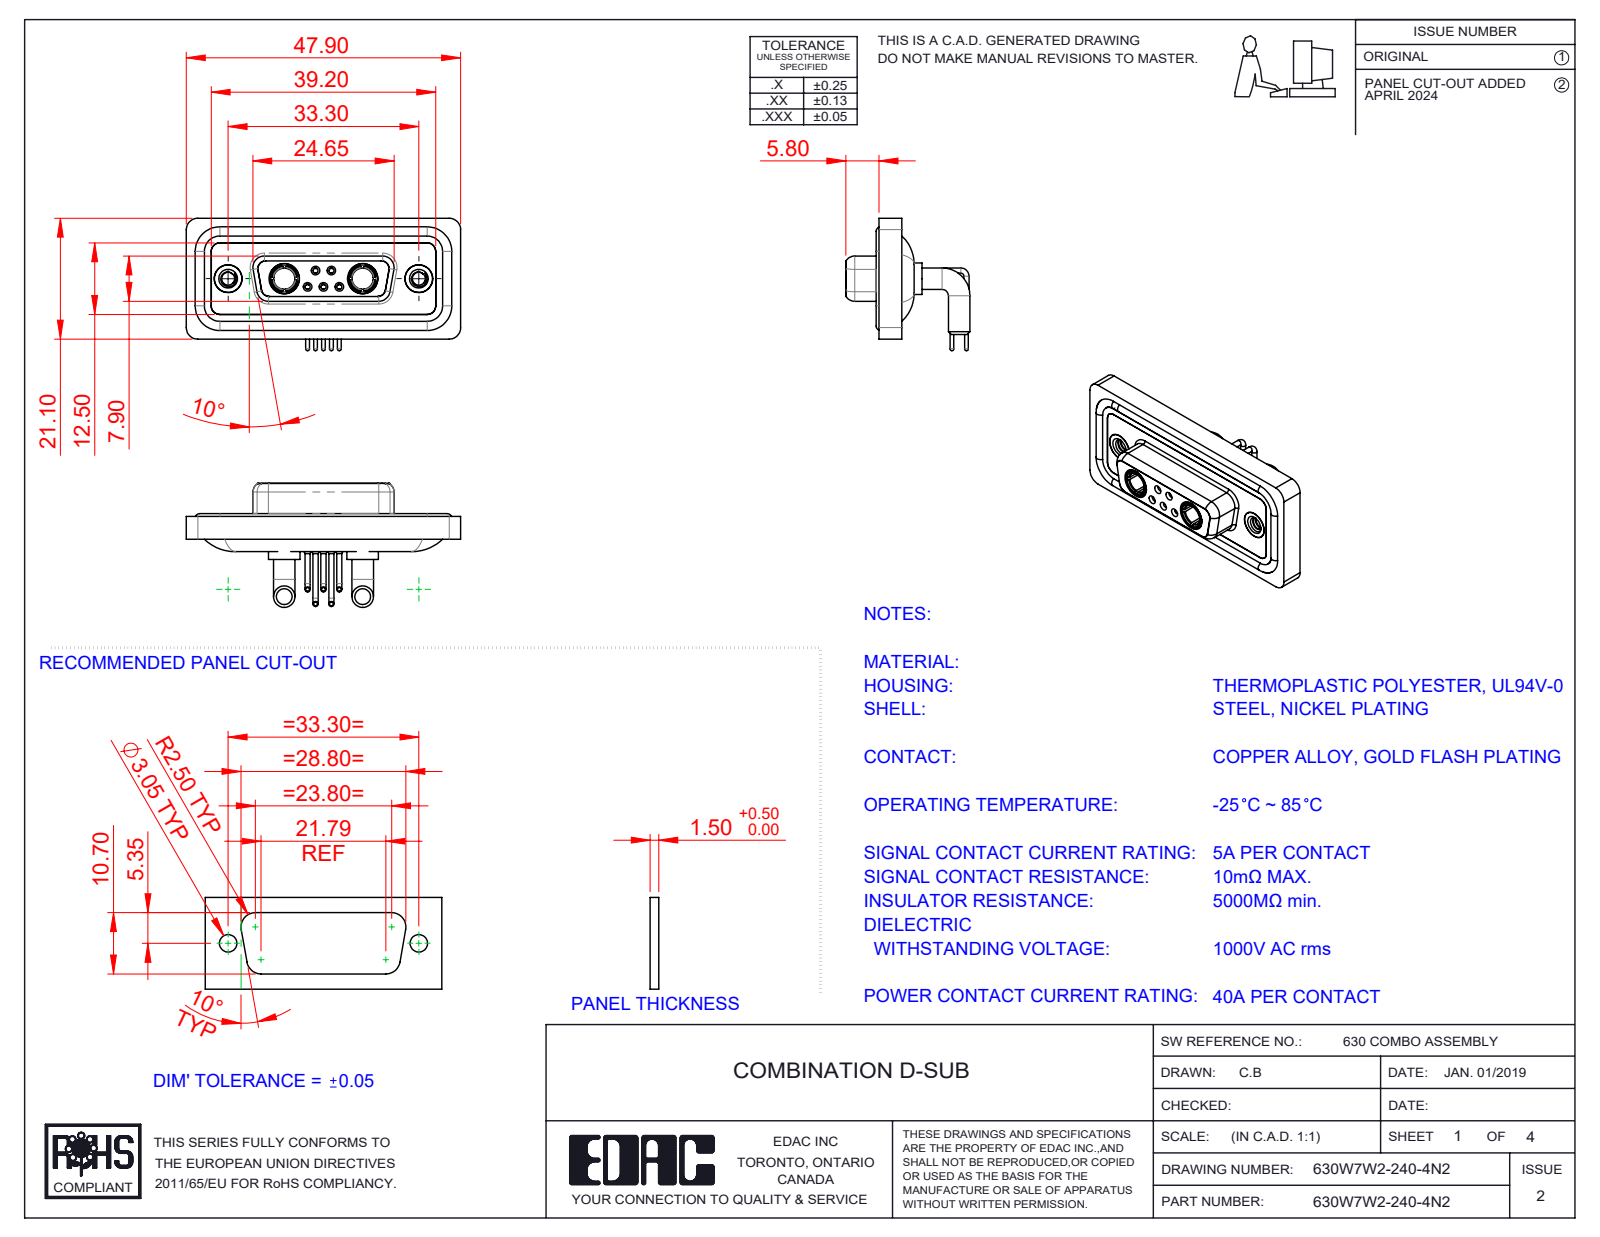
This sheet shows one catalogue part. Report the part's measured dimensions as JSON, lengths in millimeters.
{"part_name": "630Combo Waterproof Housing_15 Contacts; 630Combo Housing_7W2; 630Combo Contact Row 1_50 Contacts; Power Socket_40A RA (+5 more)", "step_written_by": "SolidWorks 2023 (CONFIG_CONTROL_DESIGN)", "units": "millimeters", "bodies": {"solids": 16, "faces": 807, "planar": 238, "cylindrical": 353, "other": 216}, "overall_size": [47.9, 23.12, 21.68], "volume_mm3": 6342, "surface_area_mm2": 10293, "round_holes": [[0.9, 5], [1.1, 5], [1.5, 5], [2, 5], [4.85, 4], [1.6, 3], [1.7, 2], [2.26, 2], [3.7, 2], [4, 2], [4.05, 2], [5, 2]], "round_bosses_or_shafts": [[1.6, 6], [0.9, 5], [0.65, 5], [3.75, 4], [5.5, 2], [5.2, 2], [4.96, 2], [4.95, 2]], "partial_cylinders_radius": [[2, 20], [1.5, 18], [1.35, 12], [1.6, 8], [0.25, 4], [0.5, 4], [0.6, 4], [0.65, 4]], "face_to_face_distances": [0.4, 1.8, 1.1, 1.6, 2.5, 2.9, 3.1, 3.7, 4.1, 1.5], "hole_center_spacings": [3.16, 2.77, 9.8, 23.5, 4.31, 4.33, 5.03, 5.04]}
